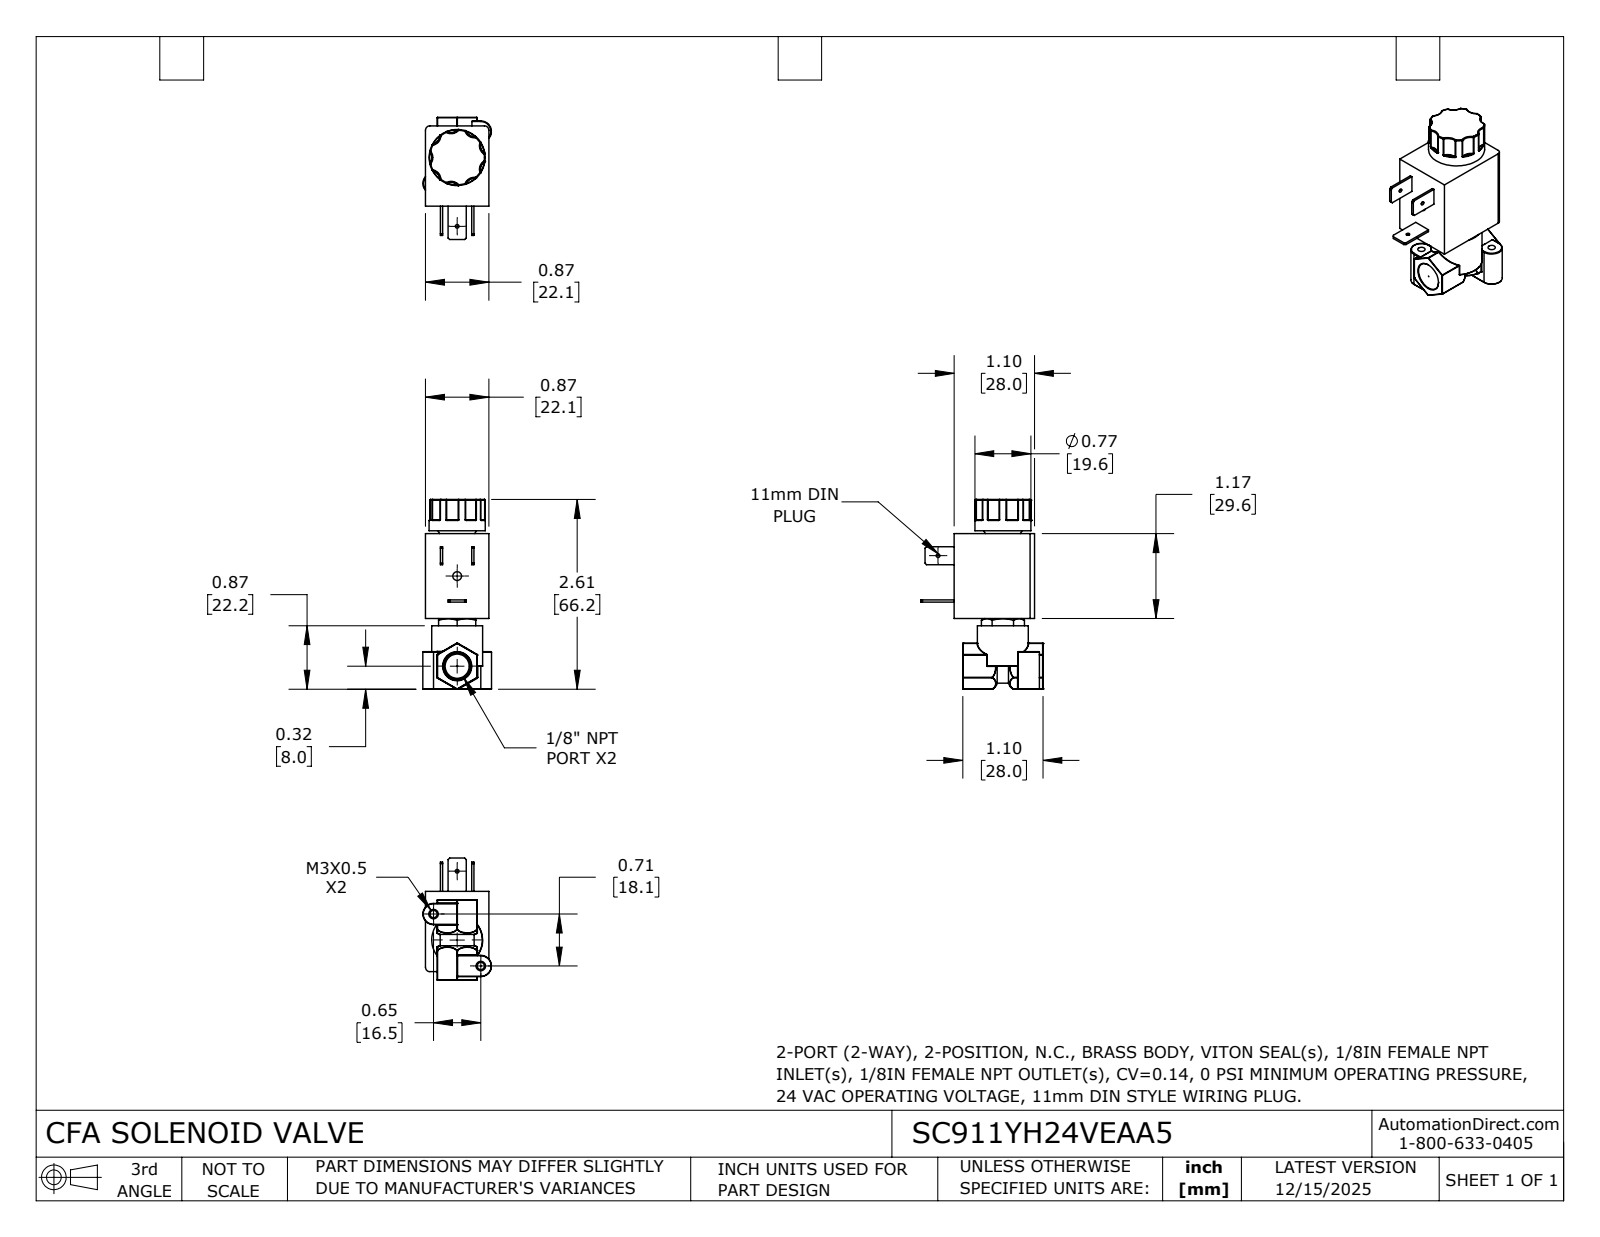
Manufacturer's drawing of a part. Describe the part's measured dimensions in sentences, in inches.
The part is named "SC911YH24VEAA5". Its 3-D file was written by "SolidWorks 2024 (CONFIG_CONTROL_DESIGN)". It is 1 solid with 393 faces: 76 planar, 108 cylindrical and 209 other. Overall it measures 2.608 by 1.678 by 0.942 inches. Its volume is 1.713 cubic inches and its surface area 14.37 square inches. Round holes: 2 of diameter 0.05, 2 of diameter 0.1, 1 of diameter 0.12. Round bosses or shafts: 1 of diameter 0.77, 1 of diameter 0.7, 1 of diameter 0.332. Partial cylindrical surfaces (rounded edges, fillets, slot ends): 27 of radius 0.004, 18 of radius 0.01, 12 of radius 0.008, 7 of radius 0.133, 2 of radius 0.017, 2 of radius 0.06, 2 of radius 0.132, 2 of radius 0.146. The main face-to-face distances are 0.87, 1.104, 1.167, 1.637, 0.47, 0.548, 0.161, 0.709, 1.207, 0.04. The hole center spacings are 0.672, 0.965, 1.342.
